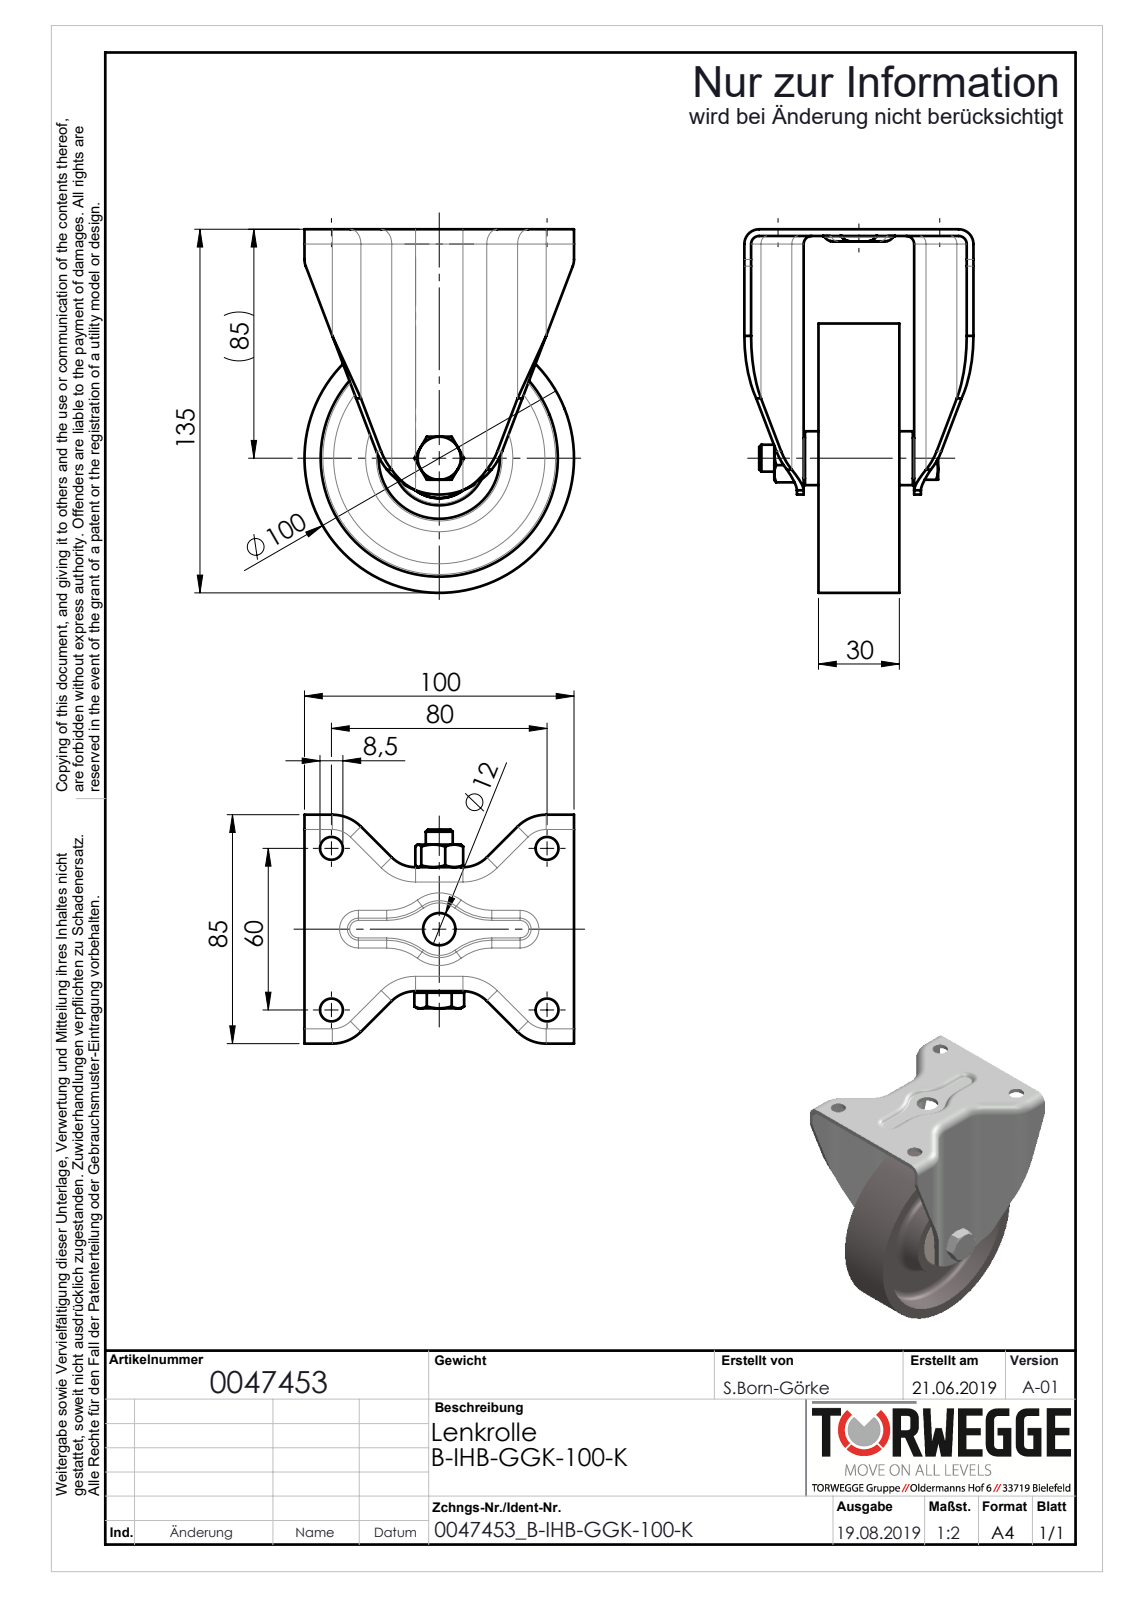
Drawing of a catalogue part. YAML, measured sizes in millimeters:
part_name: "0047453_B-IHB-GGK-100-K_(A-01)"
step_written_by: "SolidWorks 2018 (AUTOMOTIVE_DESIGN)"
units: millimeters
bodies: {solids: 17, faces: 422, planar: 110, cylindrical: 166, other: 146}
overall_size: [135, 100, 85]
volume: 180429
surface_area: 104033
round_holes:
  - {diameter: 8.5, count: 5}
  - {diameter: 10, count: 1}
  - {diameter: 10.5, count: 1}
  - {diameter: 12, count: 1}
  - {diameter: 15, count: 1}
  - {diameter: 15.5, count: 1}
  - {diameter: 20.3, count: 1}
  - {diameter: 28.48, count: 1}
  - {diameter: 29.7, count: 1}
  - {diameter: 30, count: 1}
  - {diameter: 35, count: 1}
round_bosses_or_shafts:
  - {diameter: 100, count: 1}
  - {diameter: 21.52, count: 1}
  - {diameter: 20, count: 1}
  - {diameter: 16, count: 1}
partial_cylinders:
  - {radius: 3, count: 8}
  - {radius: 5.5, count: 8}
  - {radius: 12.5, count: 8}
  - {radius: 15, count: 8}
  - {radius: 1, count: 4}
  - {radius: 3.5, count: 4}
  - {radius: 7, count: 2}
  - {radius: 25, count: 1}
face_to_face_distances: [2.5, 17, 13, 10.28, 19, 8, 25, 38, 22.5, 21]
hole_center_spacings: [50, 60, 80, 100]
